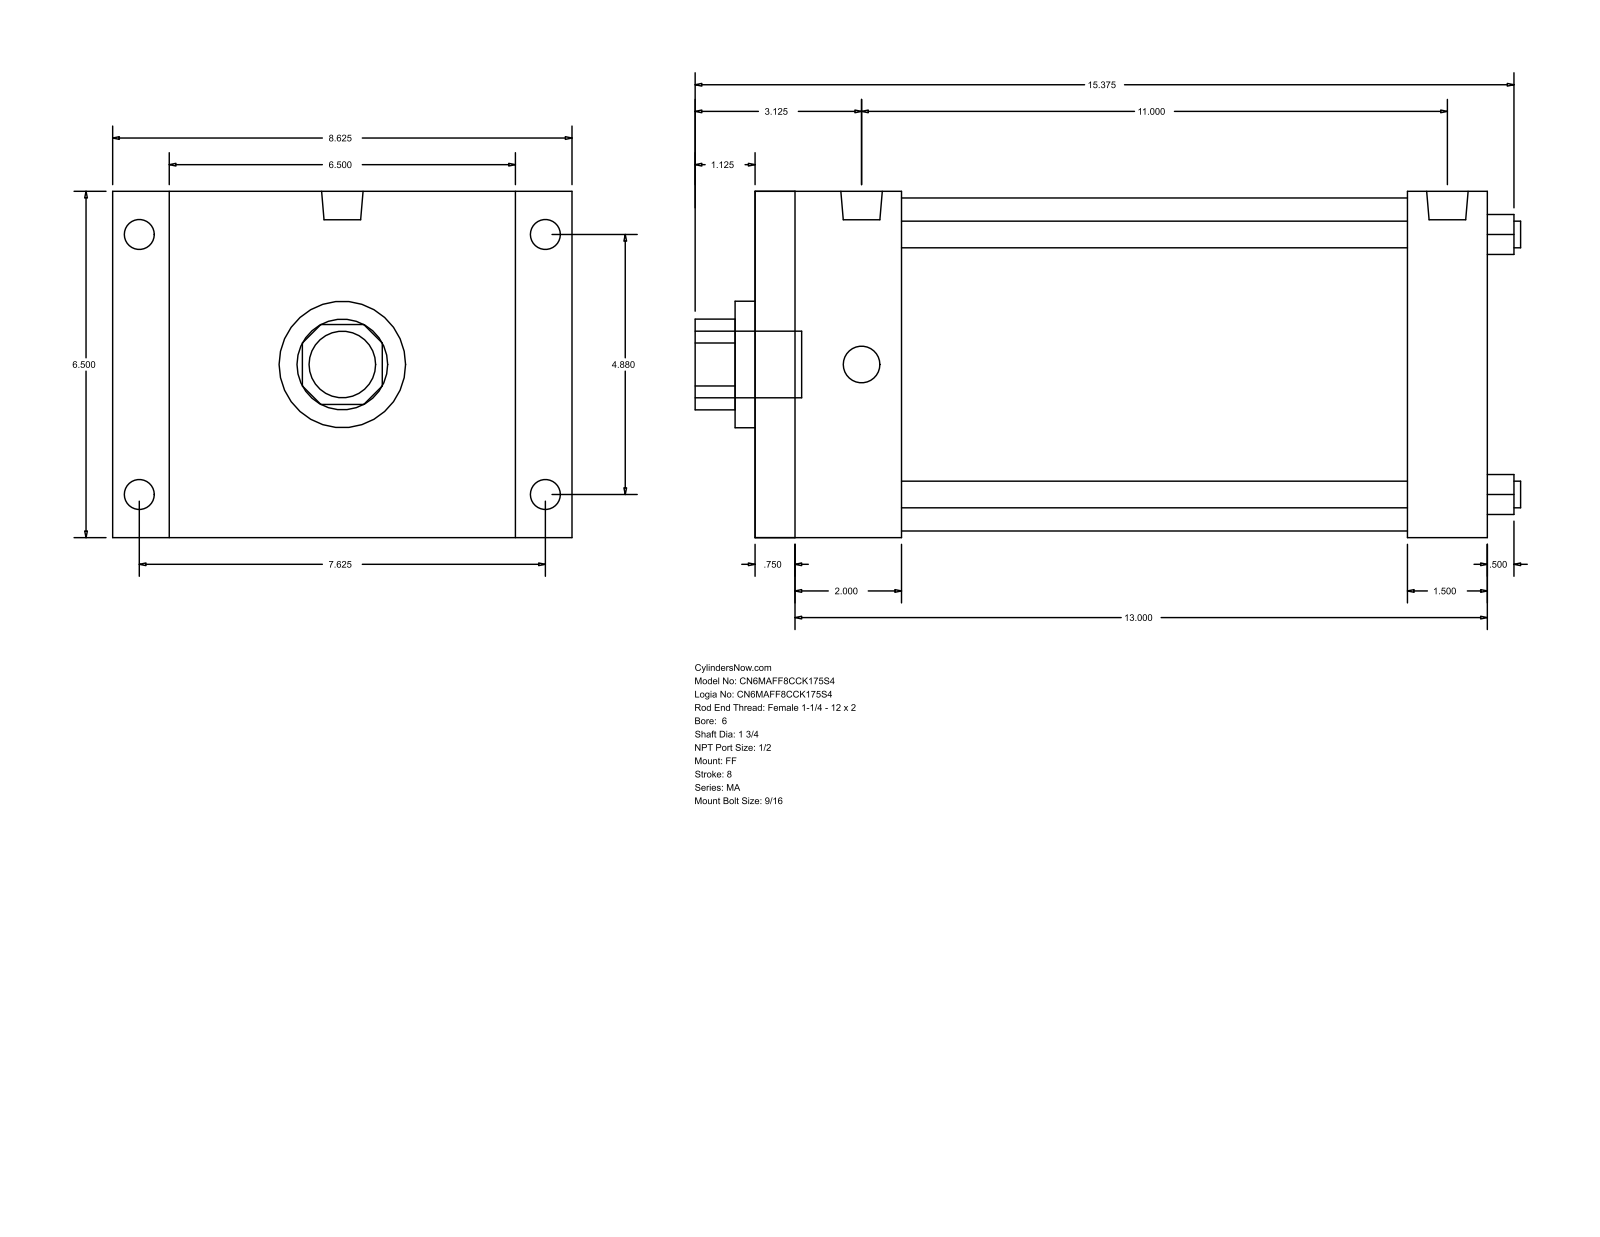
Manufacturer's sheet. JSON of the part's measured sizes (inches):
{"part_name": "MA_FF__0600_1.75", "step_written_by": "GSSL Pune (CONFIG_CONTROL_DESIGN)", "units": "inches", "bodies": {"solids": 0, "faces": 92, "planar": 64, "cylindrical": 28, "other": 0}, "overall_size": [15.5, 8.625, 6.5], "round_holes": [[0.5, 4], [1.75, 1], [2.375, 1], [6.25, 1]], "round_bosses_or_shafts": [[0.687, 4], [0.563, 4], [0.778, 2], [1.25, 1]], "partial_cylinders_radius": [[0.852, 1]], "face_to_face_distances": [6.5, 13.75, 0.75, 13, 2, 2.75, 11, 12.25, 11.5, 9.5], "hole_center_spacings": [3.451, 4.88, 6.902]}
